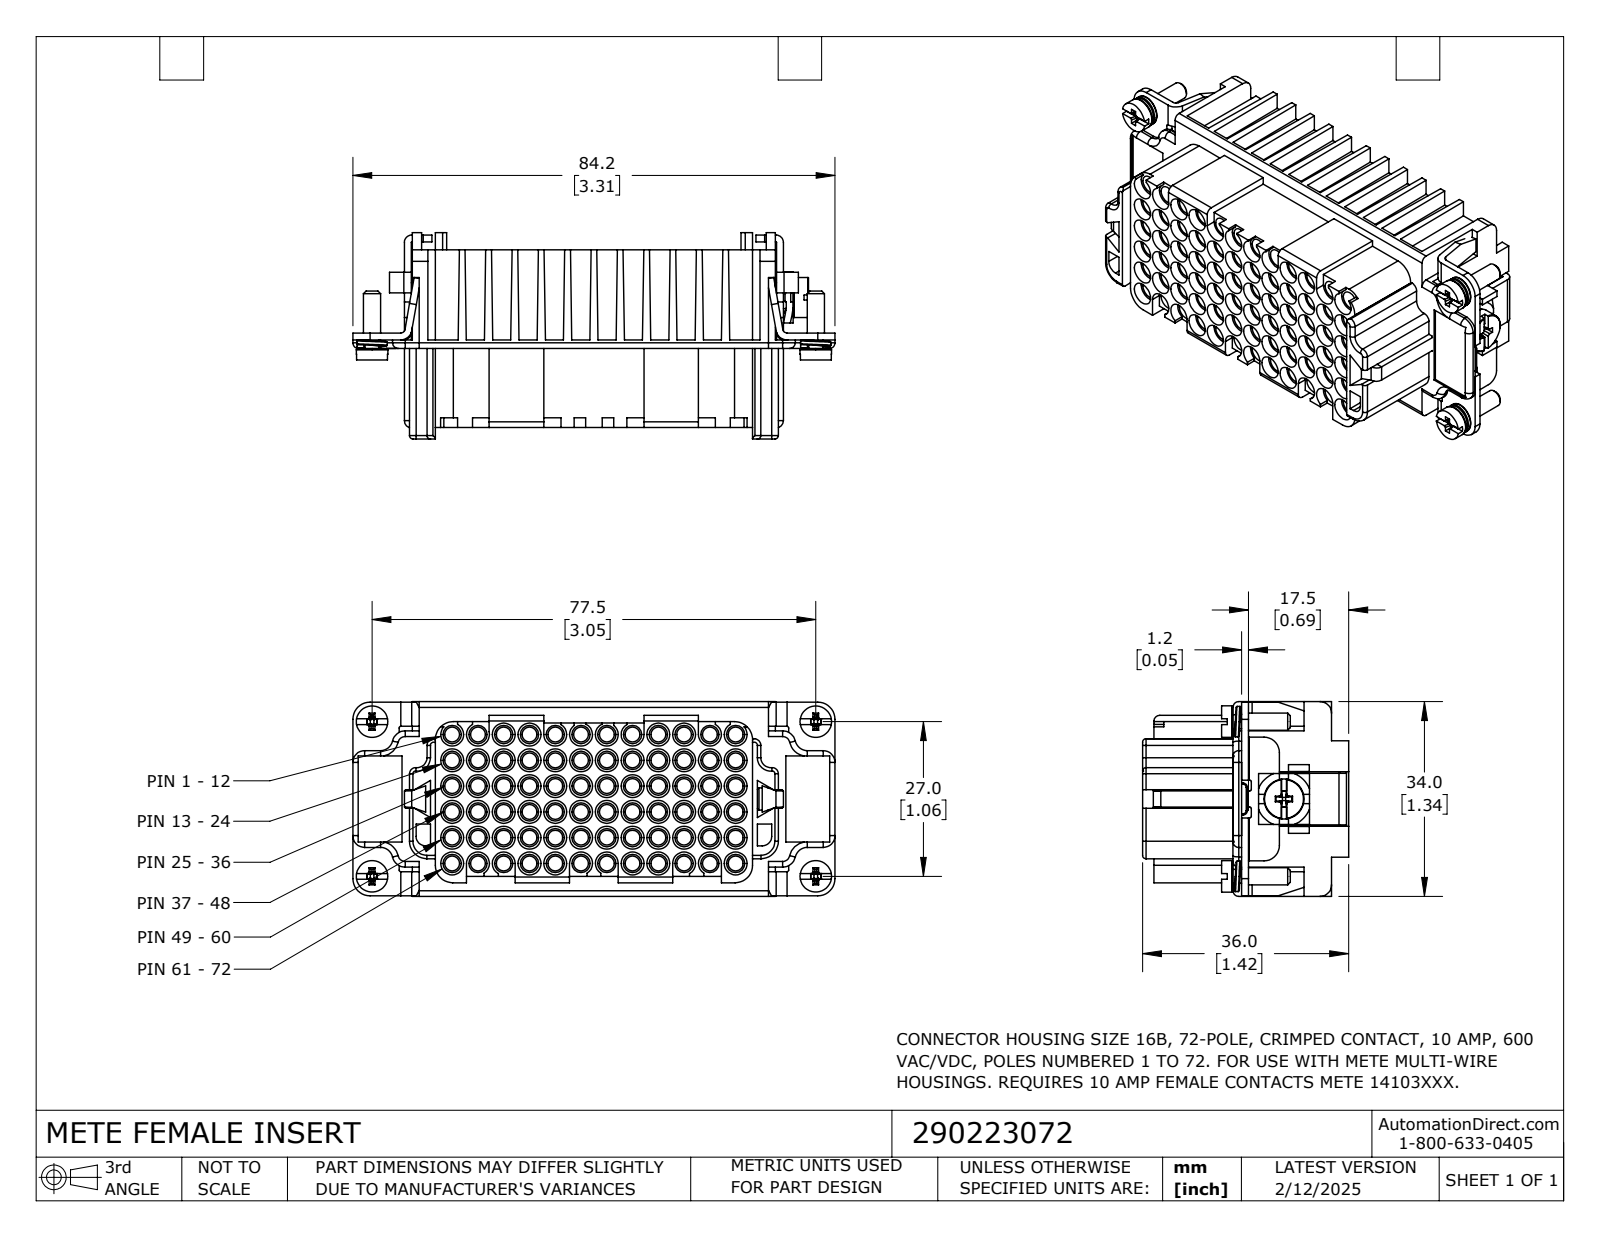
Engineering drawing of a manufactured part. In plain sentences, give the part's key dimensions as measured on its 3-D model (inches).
The part is named "290223072". Its 3-D file was written by "SolidWorks 2024 (CONFIG_CONTROL_DESIGN)". It is 13 solids with 1938 faces: 872 planar, 969 cylindrical and 97 other. Overall it measures 3.315 by 1.417 by 1.339 inches. Its volume is 2.148 cubic inches and its surface area 67.83 square inches. Round holes: 72 of diameter 0.102, 72 of diameter 0.126, 72 of diameter 0.138, 72 of diameter 0.157, 4 of diameter 0.114, 1 of diameter 0.13. Round bosses or shafts: 4 of diameter 0.217, 4 of diameter 0.209, 4 of diameter 0.118, 4 of diameter 0.096, 1 of diameter 0.276, 1 of diameter 0.201, 1 of diameter 0.154. Partial cylindrical surfaces (rounded edges, fillets, slot ends): 32 of radius 0.01, 12 of radius 0.008, 12 of radius 0.012, 10 of radius 0.004, 10 of radius 0.039, 10 of radius 0.051, 8 of radius 0.006, 8 of radius 0.02. The main face-to-face distances are 0.543, 0.181, 0.047, 0.362, 0.724, 0.118, 0.906, 0.059, 0.106, 1.22. The hole center spacings are 0.177, 0.354, 0.531, 0.886, 0.396, 0.56, 0.25, 0.73.
